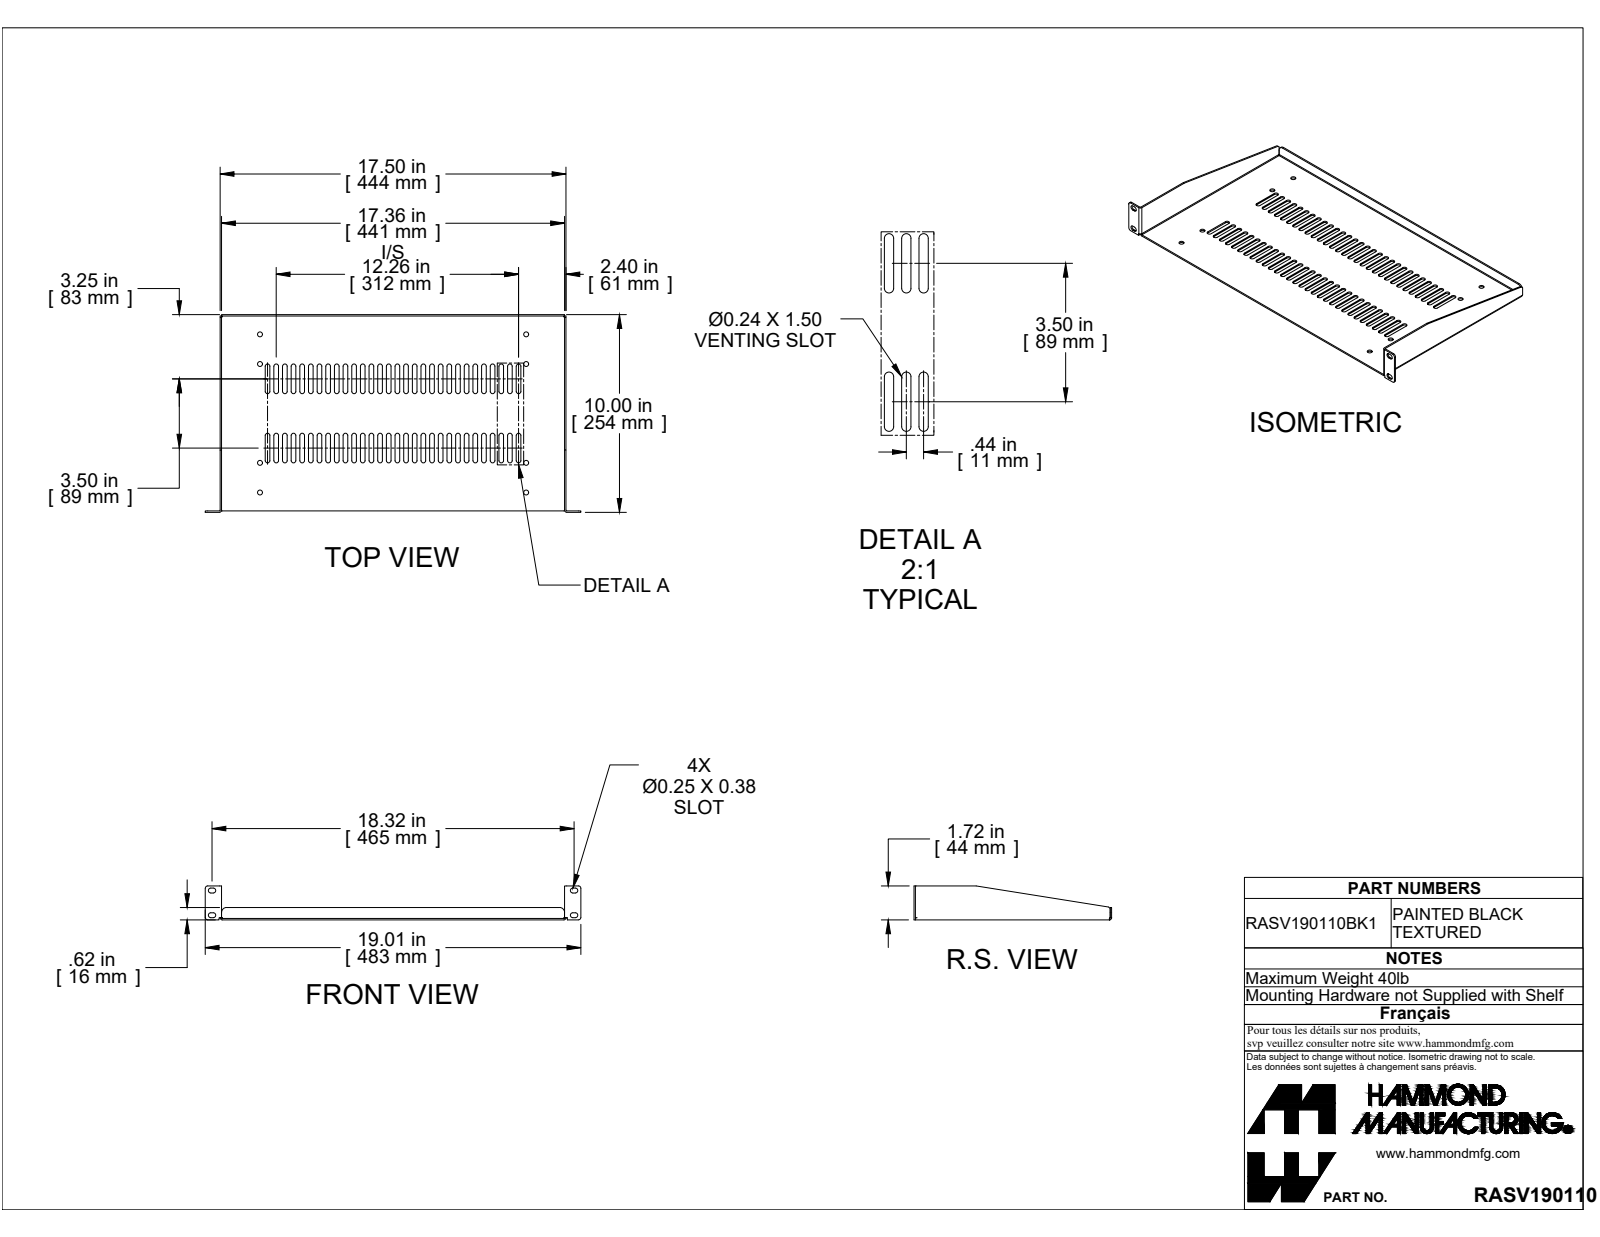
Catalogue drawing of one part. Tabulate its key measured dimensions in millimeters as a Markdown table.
| quantity | value |
| --- | --- |
| part name | RASV190110BK1 |
| STEP written by | SolidWorks 2019 (CONFIG_CONTROL_DESIGN) |
| units | millimeters |
| bodies | 1 solid, 328 faces (168 planar, 156 cylindrical, 4 other) |
| overall size | 482.8 × 254 × 43.6 |
| volume | 222 700 mm³ |
| surface area | 256 100 mm² |
| round holes (diameter × count) | 6.4 × 8 |
| partial cylindrical surfaces (radius × count) | 3 × 116, 3.2 × 12, 0.9 × 5, 2.7 × 5, 3 × 4, 1.4 × 3, 6.4 × 2 |
| main face-to-face distances | 1.8, 442.7, 440.8, 444.5, 250.3, 252.2, 22.3, 44.5, 1.8, 252.2 |
| hole center spacings | 38.1, 165.1, 342.1, 344.2, 379.8, 127, 203.2, 364.9 |
